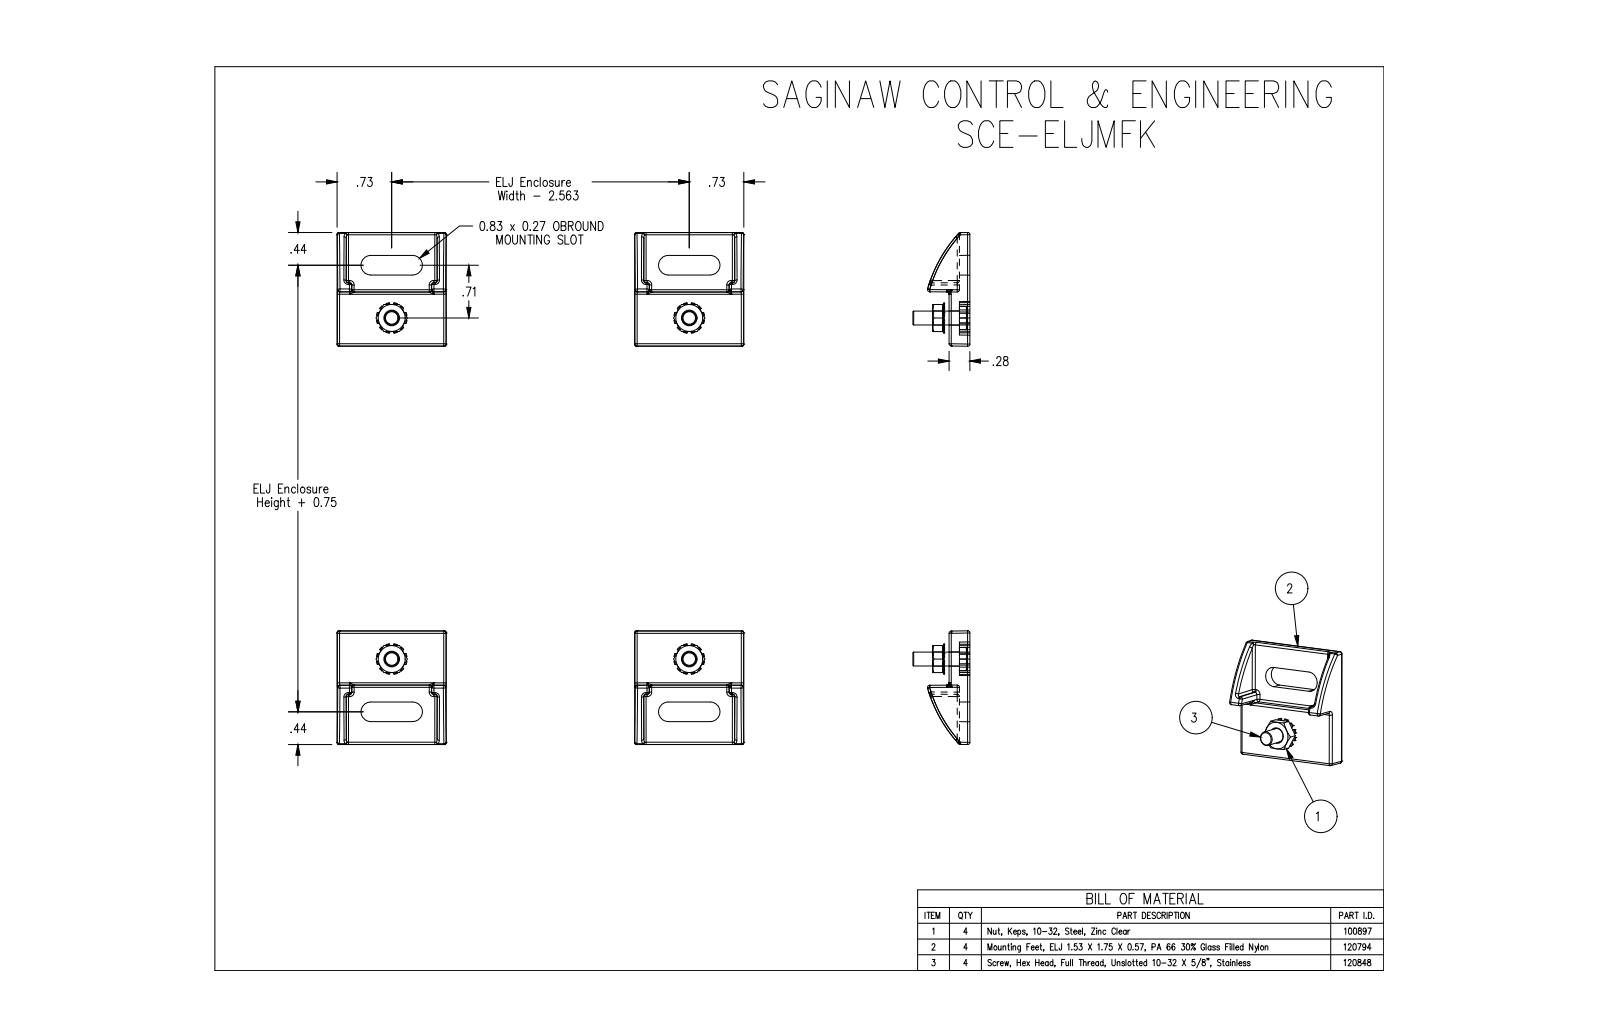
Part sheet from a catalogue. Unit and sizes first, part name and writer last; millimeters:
Units: millimetres
Overall size (bounding box): 174.7 × 138.9 × 19.5
Round holes (diameter × count): ⌀4.8 ×4, ⌀7.6 ×4
Round bosses / shafts (diameter × count): ⌀8 ×4, ⌀4.7 ×4
Partial cylindrical surfaces — rounded edges, fillets, slot ends (radius × count): R0.8 ×162
Main face-to-face distances: 7.1, 3.6, 3.6, 101.6, 3.6, 3.5, 58.2, 116.4, 7.2, 123.6
Hole centre spacings: 101.6, 116.4, 154.5
Volume: 31 430 mm³ · Surface area: 21 610 mm²
Bodies: 12 solids, 972 faces (468 planar, 240 cylindrical, 264 other)
Part name (STEP PRODUCT): SCE-ELJMFK
STEP written by: SolidWorks 2019 (CONFIG_CONTROL_DESIGN)
